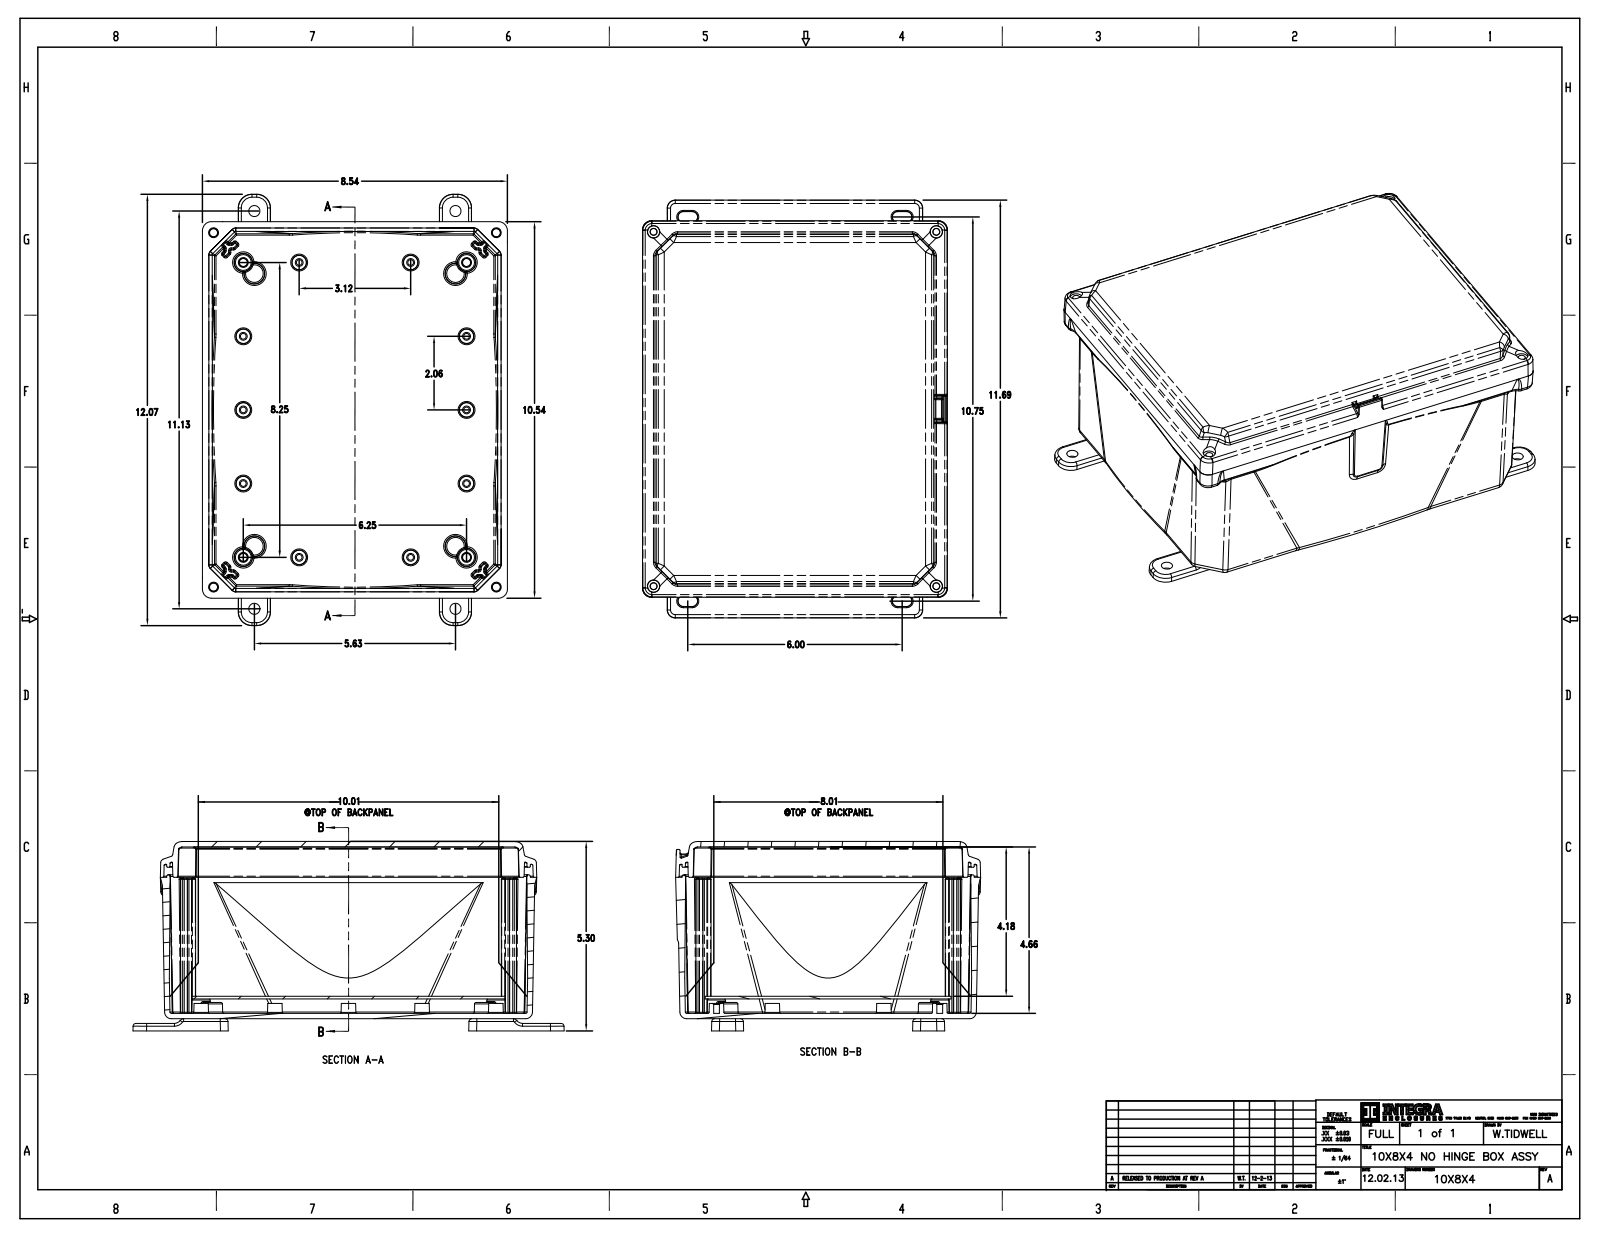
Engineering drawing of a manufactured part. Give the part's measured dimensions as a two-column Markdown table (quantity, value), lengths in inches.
| quantity | value |
| --- | --- |
| part name | H1084BS; 9912525-80-10; 9912521-80-10; H1084BS_ASM (+5 more) |
| STEP written by | CREO PARAMETRIC BY PTC INC, 2016050 (CONFIG_CONTROL_DESIGN) |
| units | inches |
| bodies | 24 solids, 3570 faces (846 planar, 1470 cylindrical, 1254 other) |
| overall size | 11.69 × 8.536 × 5.465 |
| volume | 63.47 in³ |
| surface area | 869.1 in² |
| round holes (diameter × count) | 0.16 × 10, 0.19 × 8, 0.201 × 4 |
| round bosses / shafts (diameter × count) | 0.25 × 12, 0.3 × 8, 0.298 × 8, 0.29 × 8, 0.26 × 8, 0.258 × 8, 0.375 × 4, 0.372 × 4 |
| partial cylindrical surfaces (radius × count) | 0.03 × 317, 0.02 × 168, 0.005 × 48, 0.09 × 38, 0.04 × 36, 0.1 × 28, 0.08 × 26, 0.2 × 20 |
| main face-to-face distances | 0.15, 0.49, 0.12, 3.81, 3.96, 0.392, 0.27, 4.08, 0.34, 0.098 |
| hole center spacings | 9.916, 6.25, 0.439, 1.178, 1.293, 1.565, 1.616, 1.782 |
